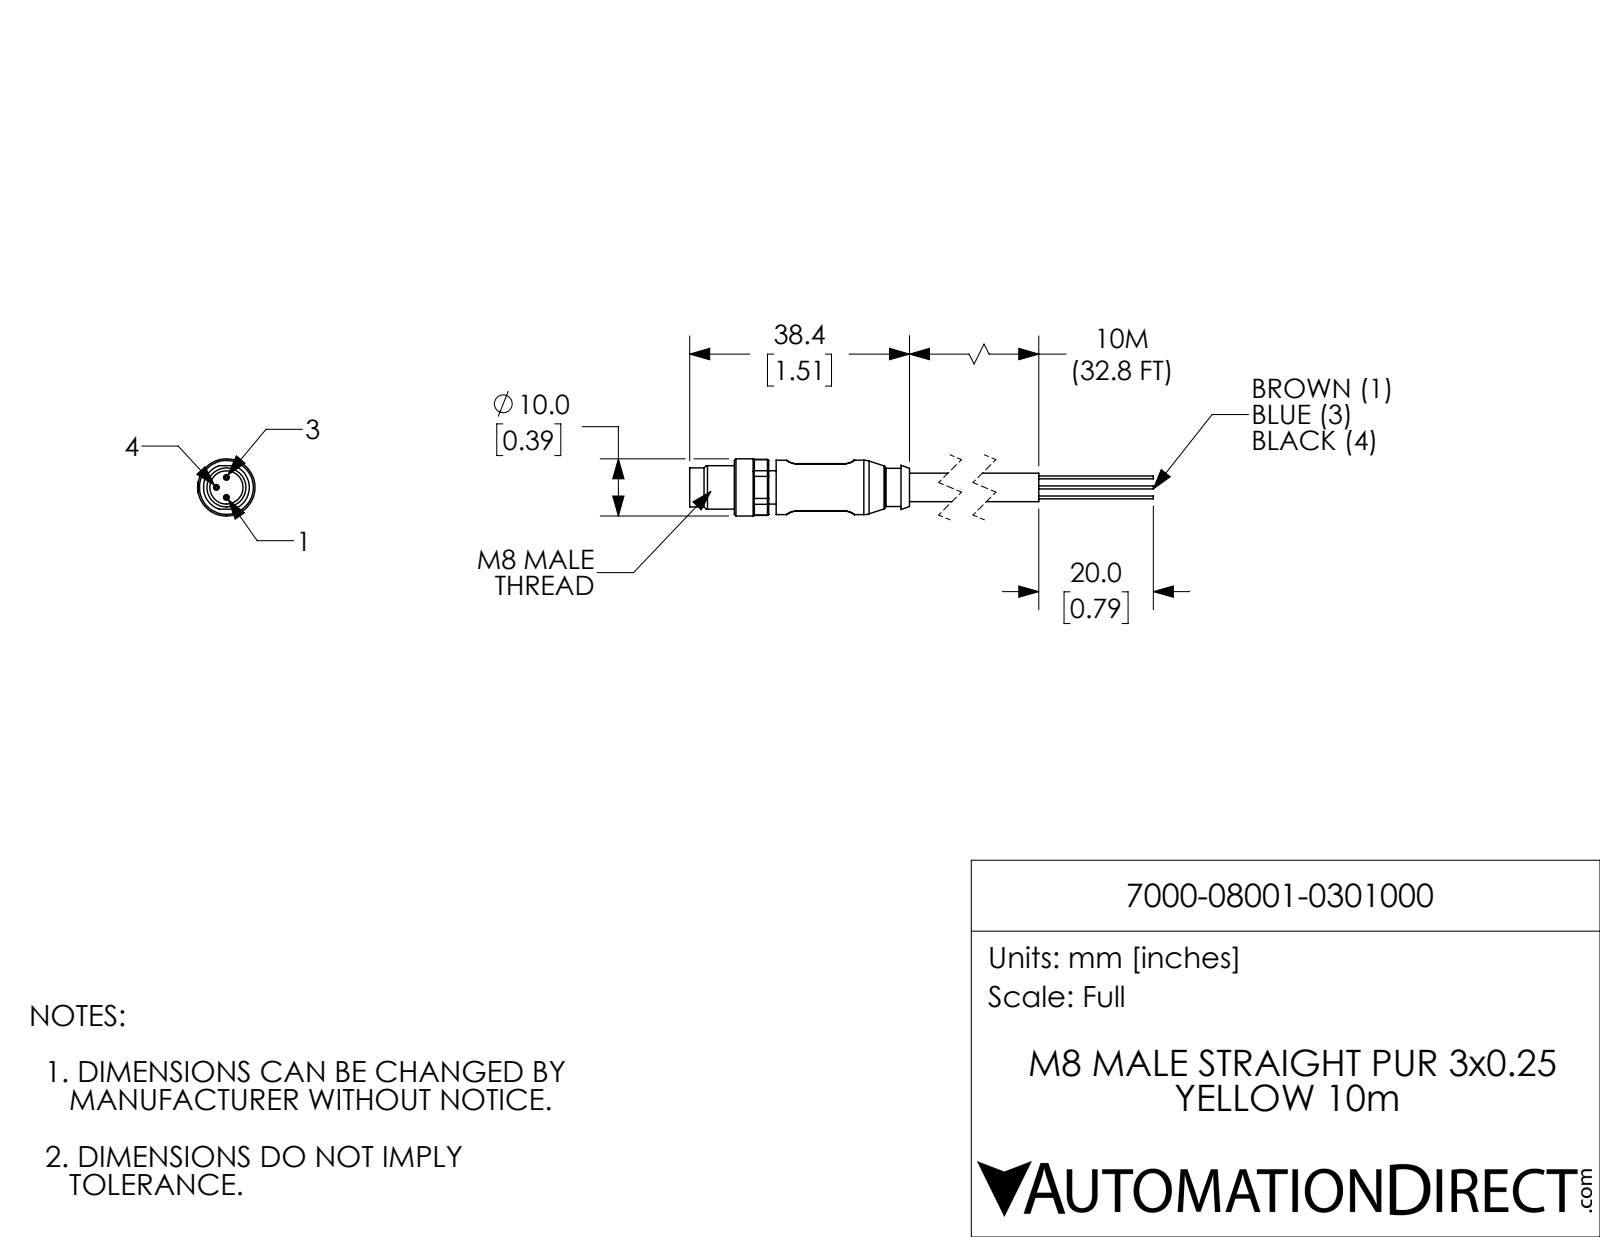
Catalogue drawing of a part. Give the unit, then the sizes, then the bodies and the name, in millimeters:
Units: millimetres
Overall size (bounding box): 78.4 × 10.05 × 10
Round holes (diameter × count): ⌀5.8 ×1
Round bosses / shafts (diameter × count): ⌀1 ×3, ⌀0.51 ×3, ⌀10 ×1, ⌀9.5 ×1, ⌀8 ×1, ⌀6.8 ×1, ⌀6.7 ×1, ⌀5 ×1
Partial cylindrical surfaces — rounded edges, fillets, slot ends (radius × count): R0.2 ×4, R2.5 ×4, R4.9 ×1, R5.05 ×1
Main face-to-face distances: 8.3, 1.3, 9, 0.35, 7.95, 8.8, 10.1, 53.4, 44.6, 43.3
Volume: 2 535 mm³ · Surface area: 1 801 mm²
Bodies: 4 solids, 119 faces (41 planar, 44 cylindrical, 34 other)
Part name (STEP PRODUCT): 7000-08001-0301000
STEP written by: SolidWorks 2021 (CONFIG_CONTROL_DESIGN)
